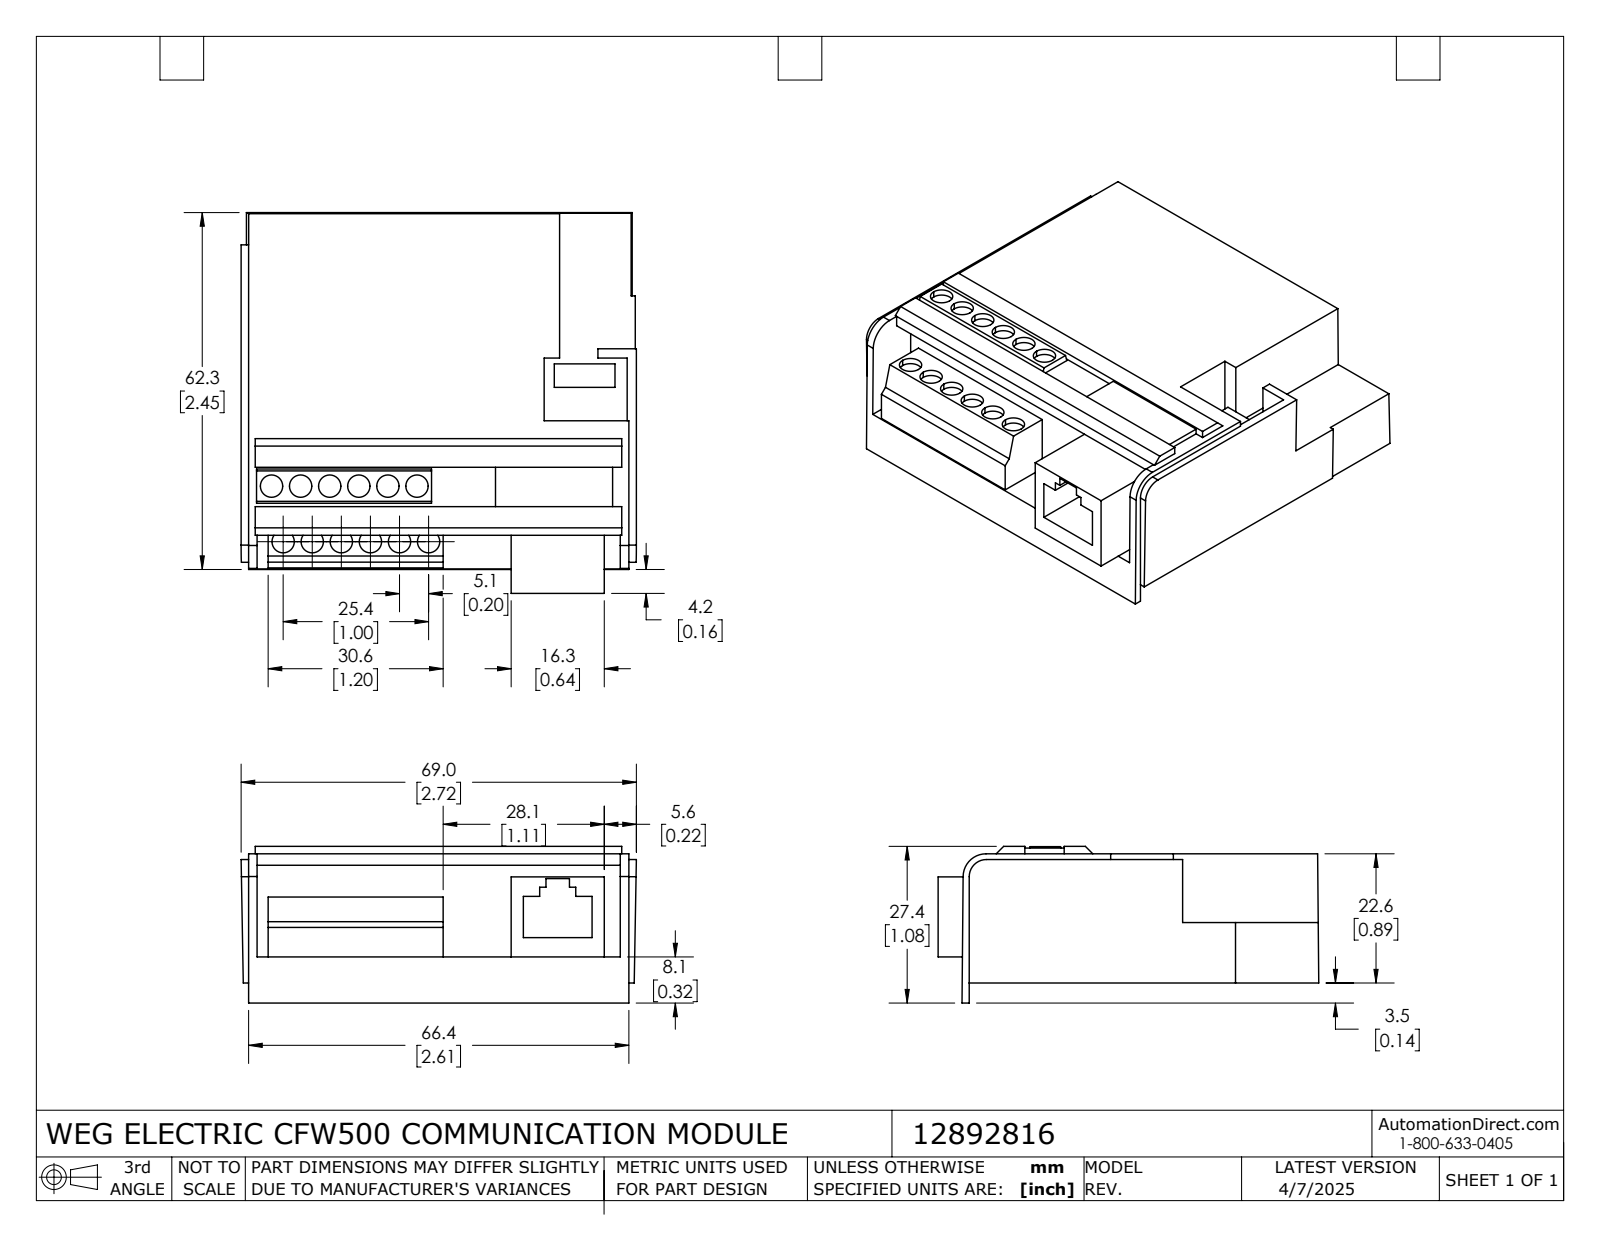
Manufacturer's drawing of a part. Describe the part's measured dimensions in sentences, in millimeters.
The part is named "12892816". Its 3-D file was written by "SolidWorks 2021 (AUTOMOTIVE_DESIGN)". It is 1 solid with 129 faces: 101 planar, 28 cylindrical and 0 other. Overall it measures 69 by 66.5 by 27.4 millimeters. Its volume is 74 070 cubic millimeters and its surface area 18 620 square millimeters. Round holes: 12 of diameter 3.9. Partial cylindrical surfaces (rounded edges, fillets, slot ends): 1 of radius 3, 1 of radius 4. The main face-to-face distances are 19.6, 1, 12, 20.9, 1.3, 8.2, 7.6, 13.3, 2, 3. The hole center spacings are 10.2, 5.1, 9.9, 15.2, 12, 12.6, 15.6, 20.3.
